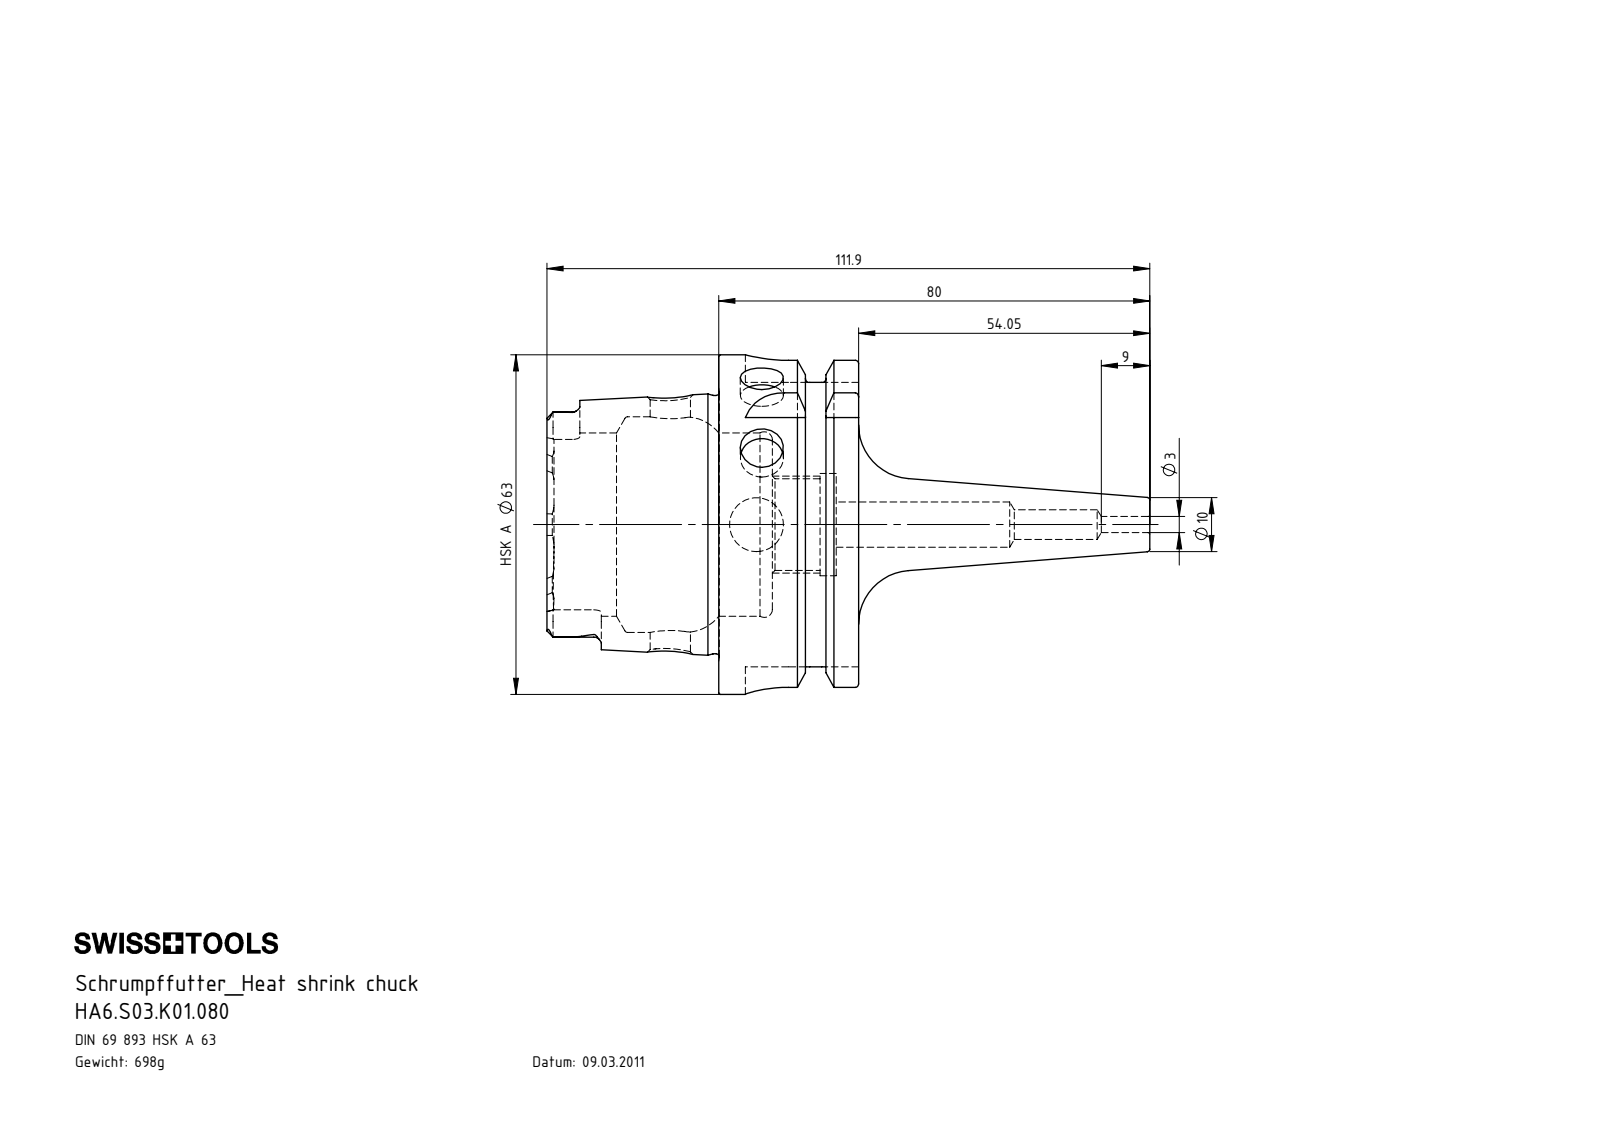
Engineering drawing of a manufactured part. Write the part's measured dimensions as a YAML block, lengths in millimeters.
part_name: "HA6.S03.K01.080"
step_written_by: "SolidWorks 2017 (AUTOMOTIVE_DESIGN)"
units: millimeters
bodies: {solids: 1, faces: 140, planar: 48, cylindrical: 35, other: 57}
overall_size: [111.9, 63, 63]
volume: 93709
surface_area: 26508
round_holes:
  - {diameter: 8, count: 2}
  - {diameter: 3, count: 1}
  - {diameter: 5.5, count: 1}
  - {diameter: 7.5, count: 1}
  - {diameter: 8.4, count: 1}
  - {diameter: 10, count: 1}
  - {diameter: 17, count: 1}
  - {diameter: 19, count: 1}
  - {diameter: 34, count: 1}
  - {diameter: 40, count: 1}
round_bosses_or_shafts:
  - {diameter: 63, count: 1}
  - {diameter: 54.95, count: 1}
  - {diameter: 47.94, count: 1}
  - {diameter: 20, count: 1}
partial_cylinders:
  - {radius: 1.4, count: 6}
  - {radius: 2.88, count: 4}
  - {radius: 8, count: 4}
face_to_face_distances: [25.95, 16, 9.95, 31.9, 41.85, 57.85, 52.8, 21.8, 11.85, 53.7]
